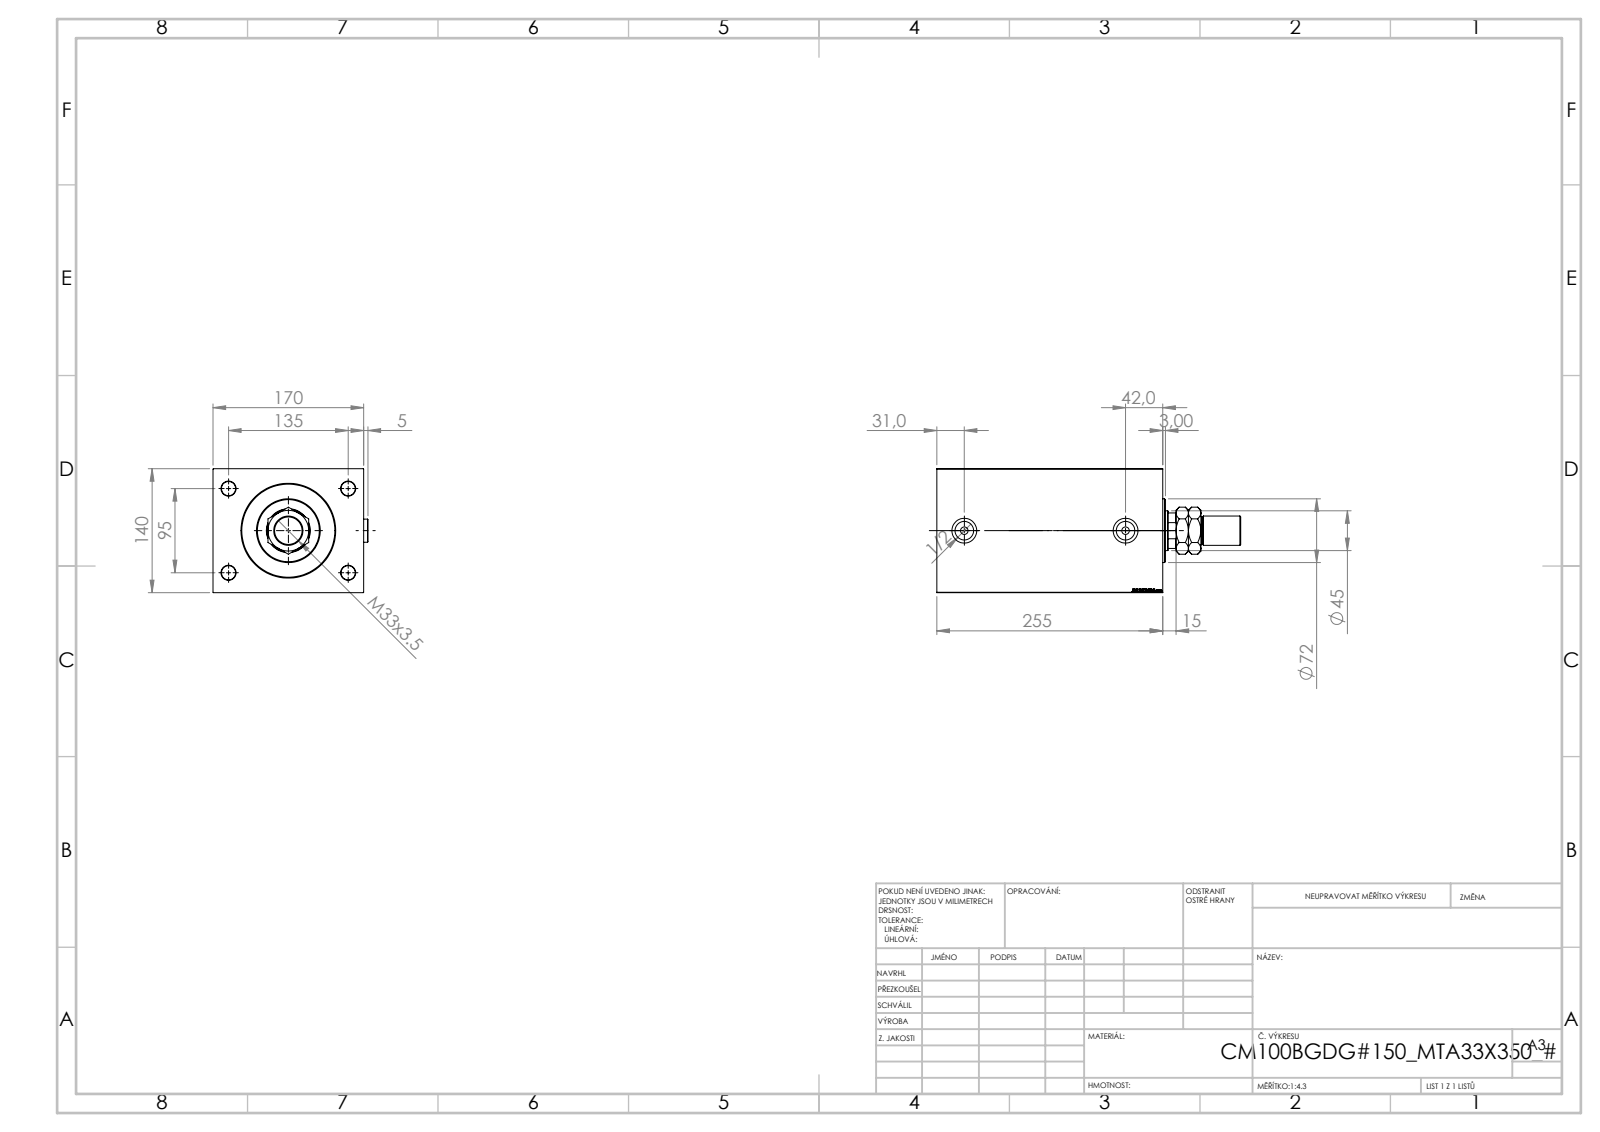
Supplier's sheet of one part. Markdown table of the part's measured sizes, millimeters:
| quantity | value |
| --- | --- |
| part name | V450CM_VC_B; Zatka_OIL_PORT; MTA; V450CM_B_VCP (+1 more) |
| STEP written by | SolidWorks 2019 (CONFIG_CONTROL_DESIGN) |
| units | millimeters |
| bodies | 6 solids, 987 faces (451 planar, 76 cylindrical, 460 other) |
| overall size | 343 × 174.9 × 140 |
| volume | 5 146 000 mm³ |
| surface area | 397 865 mm² |
| round holes (diameter × count) | 16 × 4, 8.5 × 2, 20.96 × 2, 28 × 2, 31.5 × 1, 45 × 1, 48.5 × 1, 49.5 × 1, 100 × 1, 102 × 1, 105 × 1 |
| round bosses / shafts (diameter × count) | 26 × 2, 72 × 1, 33 × 1, 31 × 1 |
| partial cylindrical surfaces (radius × count) | 22 × 1 |
| main face-to-face distances | 140, 170, 255, 229, 26, 15, 214, 240, 90, 64 |
| hole center spacings | 82.54, 95, 135, 165.08, 182 |
